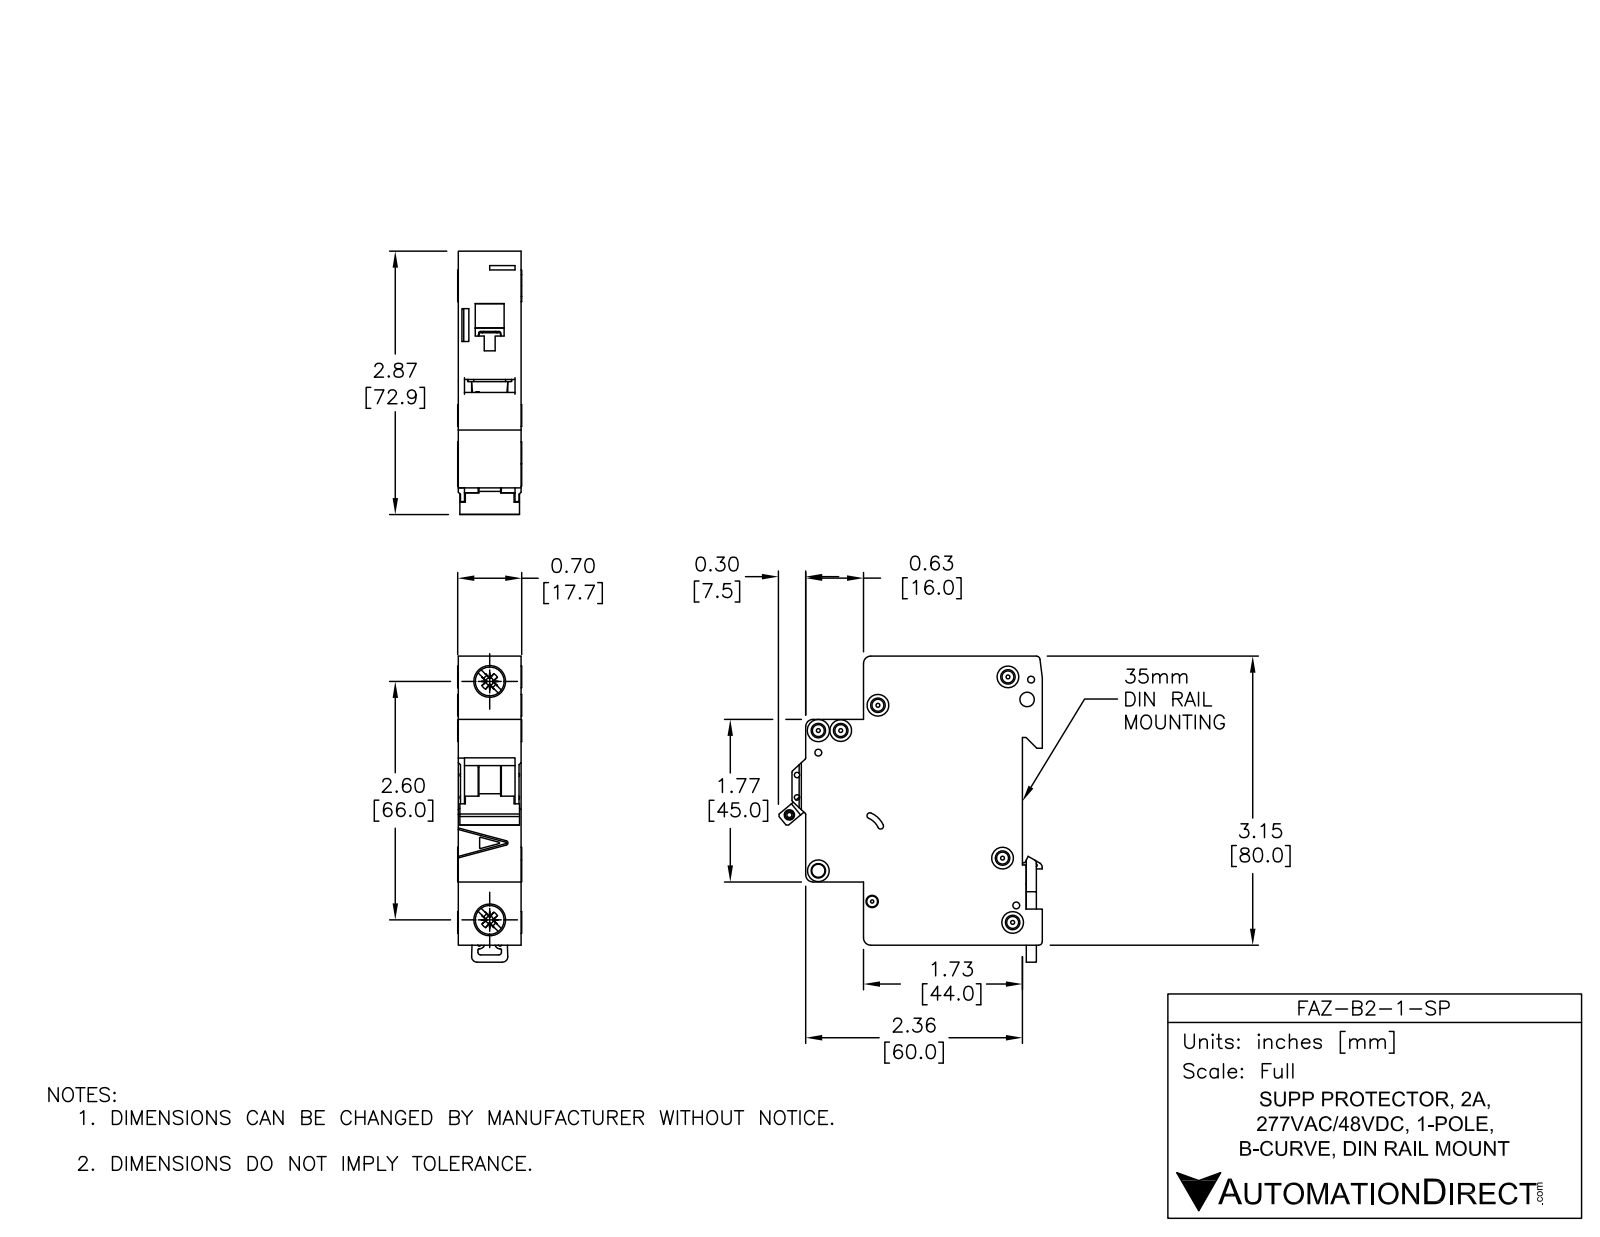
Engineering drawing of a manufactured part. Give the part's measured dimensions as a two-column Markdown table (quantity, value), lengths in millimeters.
| quantity | value |
| --- | --- |
| part name | FAZ-B2-1-SP |
| STEP written by | SolidWorks 2014 (AUTOMOTIVE_DESIGN) |
| units | millimeters |
| bodies | 5 solids, 558 faces (235 planar, 202 cylindrical, 121 other) |
| overall size | 84.78 × 73.04 × 17.7 |
| volume | 74 935 mm³ |
| surface area | 19 545 mm² |
| round holes (diameter × count) | 3.6 × 6, 1.9 × 3, 1.09 × 2, 1.5 × 2, 4 × 2, 7.15 × 2, 2.15 × 1, 2.2 × 1, 2.55 × 1, 3.3 × 1, 3.4 × 1 |
| round bosses / shafts (diameter × count) | 6 × 4, 8.2 × 2, 2.5 × 1 |
| partial cylindrical surfaces (radius × count) | 0.25 × 30, 0.5 × 13, 2 × 8, 0.2 × 5, 1 × 4, 0.8 × 2, 3 × 2, 1.5 × 1 |
| main face-to-face distances | 17.5, 79.48, 5.5, 49.5, 44, 65.5, 60, 16, 1.75, 15.75 |
| hole center spacings | 6.2, 13.64, 4.81, 5.19, 5.61, 6.1, 6.44, 8.19 |
